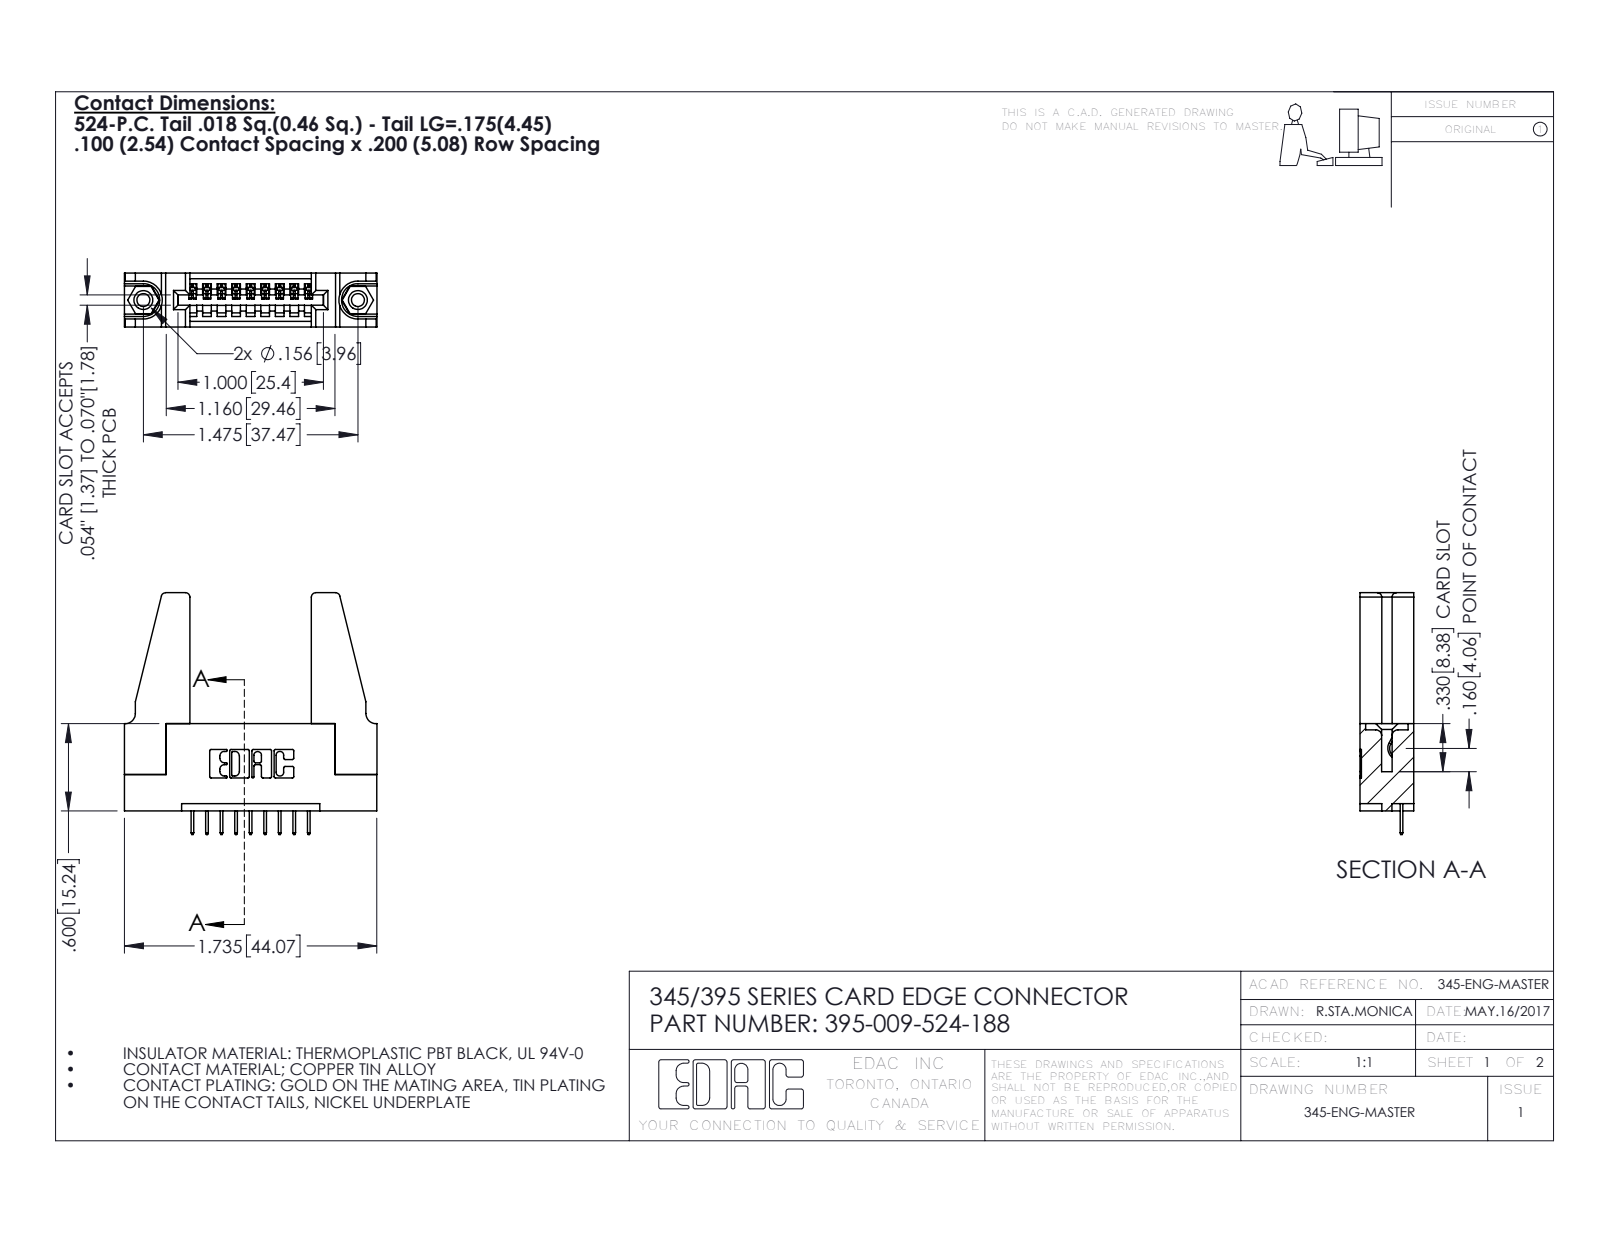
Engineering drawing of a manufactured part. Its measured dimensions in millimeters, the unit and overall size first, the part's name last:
Units: millimetres
Overall size (bounding box): 44.1 × 42.2 × 9.4
Round holes (diameter × count): ⌀2.3 ×2, ⌀3.2 ×2, ⌀4 ×2, ⌀1.6 ×1
Round bosses / shafts (diameter × count): ⌀3.9 ×2
Partial cylindrical surfaces — rounded edges, fillets, slot ends (radius × count): R0.3 ×22, R0.2 ×18, R0.8 ×8, R0.2 ×6, R0.8 ×6, R0.7 ×3, R0.8 ×2, R1 ×2
Main face-to-face distances: 9.4, 1.8, 7.6, 5.1, 2.5, 6.9, 0.6, 3.8, 3.8, 6.4
Hole centre spacings: 6.9, 31.6, 37.5
Volume: 7 130 mm³ · Surface area: 7 729 mm²
Bodies: 14 solids, 808 faces (566 planar, 226 cylindrical, 16 other)
Part name (STEP PRODUCT): 345-220-078_345-220-088; 345-250-001_345-250-001-102; 345 Part_Flush Mounting Lugs - 0.156 Dia-TH; 345-292-001_345-293-124 (+1 more)
STEP written by: SolidWorks 2016 (CONFIG_CONTROL_DESIGN)
